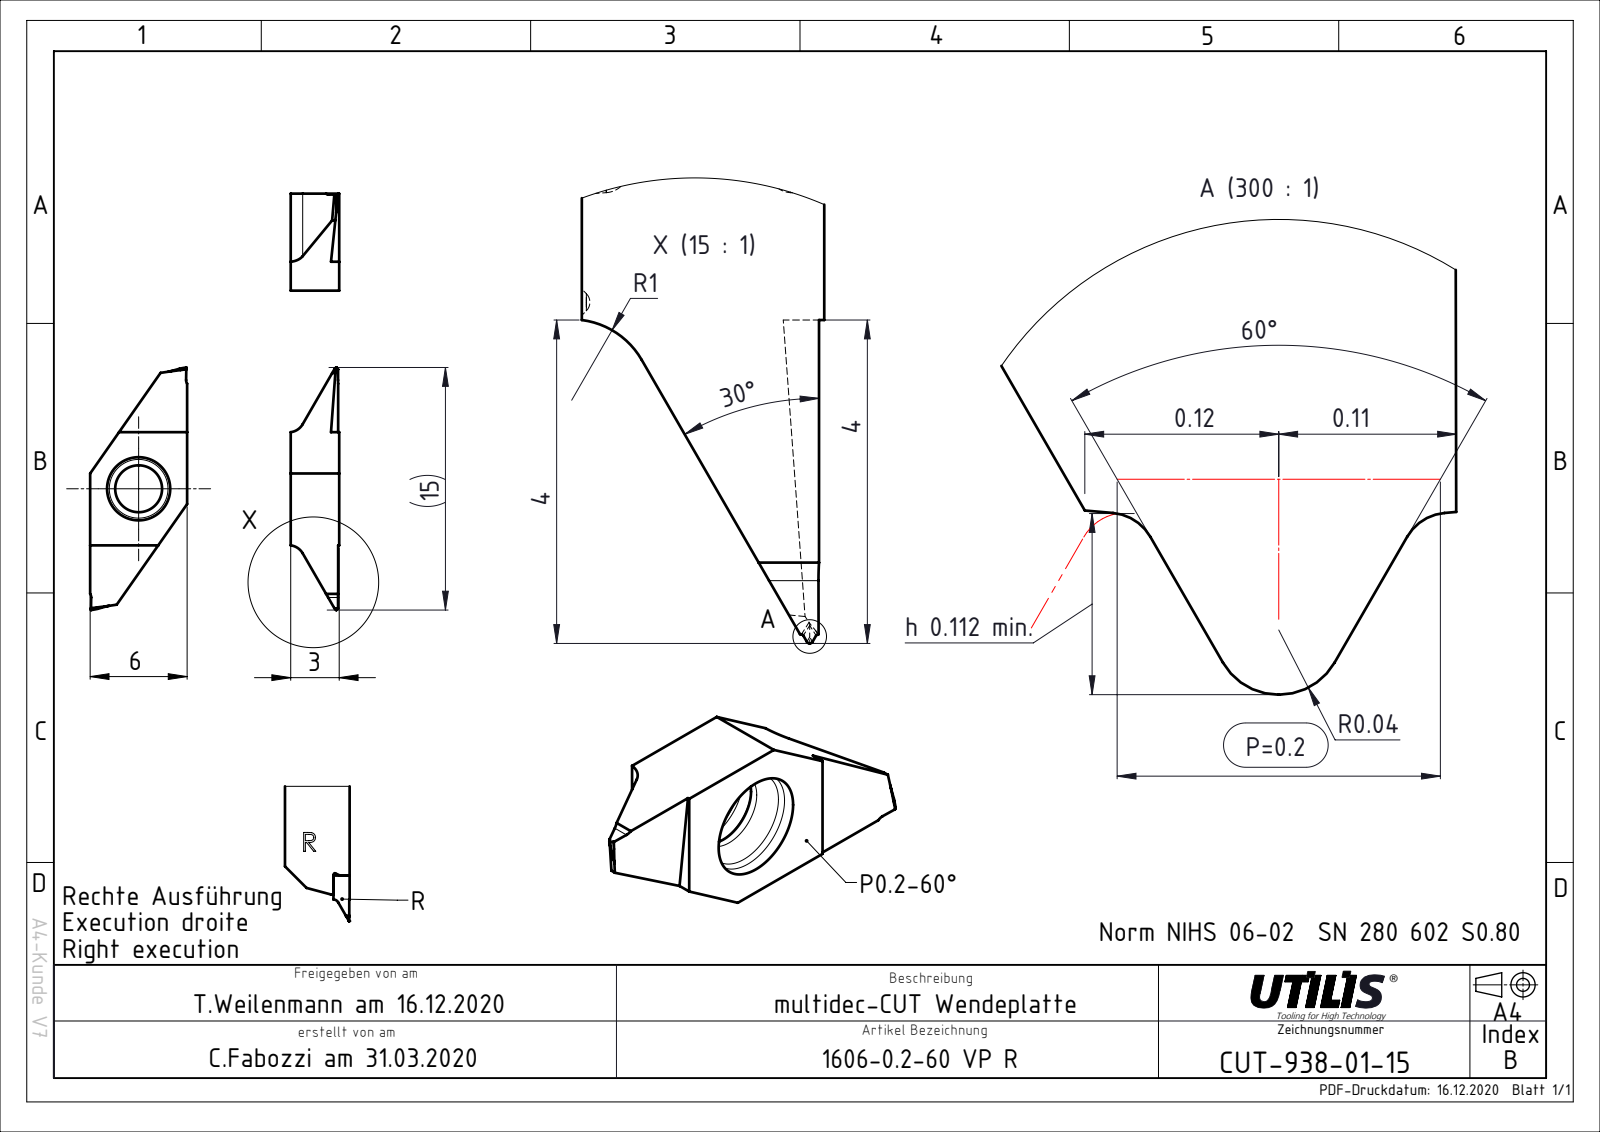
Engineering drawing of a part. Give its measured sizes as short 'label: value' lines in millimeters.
name: CUT-938-01; ASME Y14.5
written by: FormatWorks Professional (AP242_MANAGED_MODEL_BASED_3D_ENGINEERING_MIM_LF)
unit: mm
bodies: 1 solid, 36 faces (22 planar, 14 cylindrical, 0 other)
size: 15 × 6 × 3
volume: 126 mm³; area: 210 mm²
holes: 1× ⌀2.9
rounds: 2× R1
face distances: 6, 3, 9, 7, 12, 7.21, 14.41, 14.4
